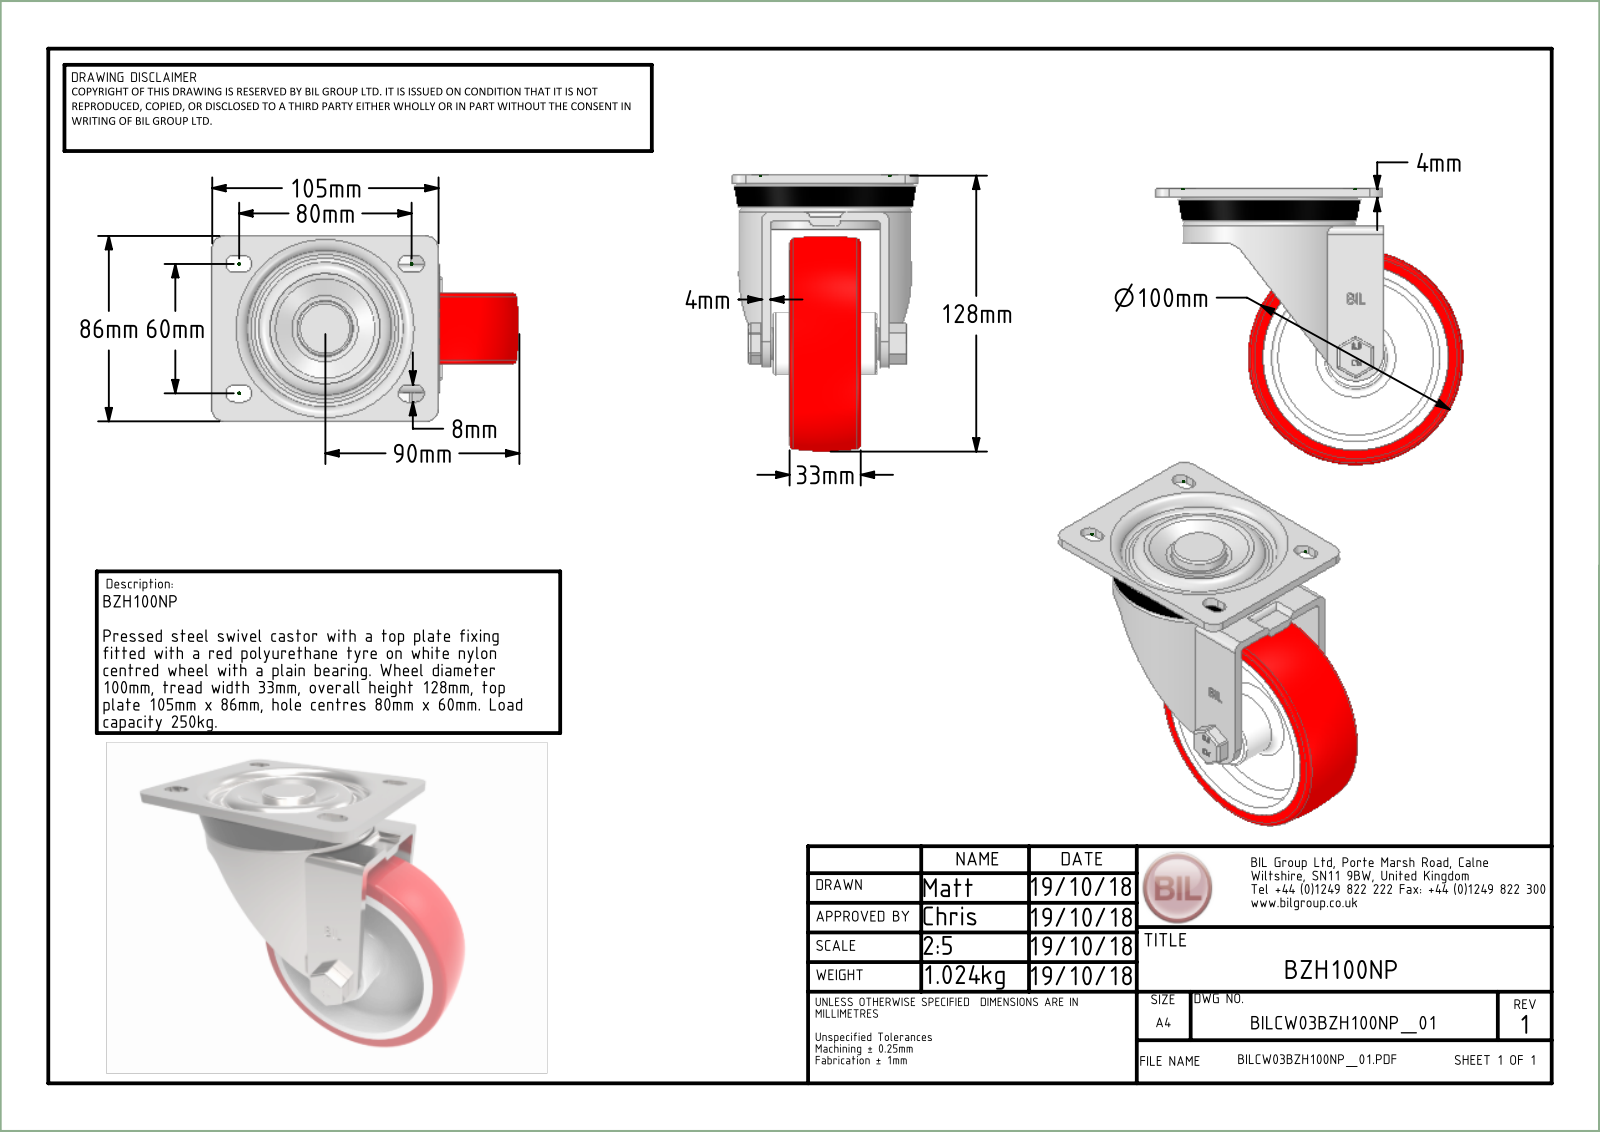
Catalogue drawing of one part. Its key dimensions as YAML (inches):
part_name: "BZH100NP v3; BZH100AS - 2 v1; ZINC PLATED, PRESSED STEEL TOP PLATE (1); ZINC PLATED, PRESSED STEEL FORKS (1) (+8 more)"
step_written_by: "Autodesk Translation Framework v14.10.0.0 (AUTOMOTIVE_DESIGN)"
units: inches
bodies: {solids: 9, faces: 386, planar: 171, cylindrical: 119, other: 96}
overall_size: [5.61, 5.039, 3.386]
volume: 18.33
surface_area: 193.3
round_holes:
  - {diameter: 0.394, count: 1}
  - {diameter: 0.402, count: 1}
  - {diameter: 0.413, count: 1}
  - {diameter: 0.472, count: 1}
  - {diameter: 0.606, count: 1}
  - {diameter: 0.984, count: 1}
  - {diameter: 1.26, count: 1}
  - {diameter: 2.835, count: 1}
  - {diameter: 3.228, count: 1}
round_bosses_or_shafts:
  - {diameter: 3.15, count: 1}
  - {diameter: 1.988, count: 1}
  - {diameter: 1.22, count: 1}
  - {diameter: 1.181, count: 1}
  - {diameter: 0.787, count: 1}
  - {diameter: 0.63, count: 1}
  - {diameter: 0.591, count: 1}
  - {diameter: 0.388, count: 1}
partial_cylinders:
  - {radius: 0.02, count: 18}
  - {radius: 0.177, count: 8}
  - {radius: 0.03, count: 6}
  - {radius: 0.079, count: 4}
  - {radius: 0.315, count: 4}
  - {radius: 0.157, count: 2}
  - {radius: 1, count: 2}
  - {radius: 0.513, count: 1}
face_to_face_distances: [0.157, 0.748, 0.551, 0.295, 0.197, 0.453, 0.354, 0.906, 0.512, 1.063]
